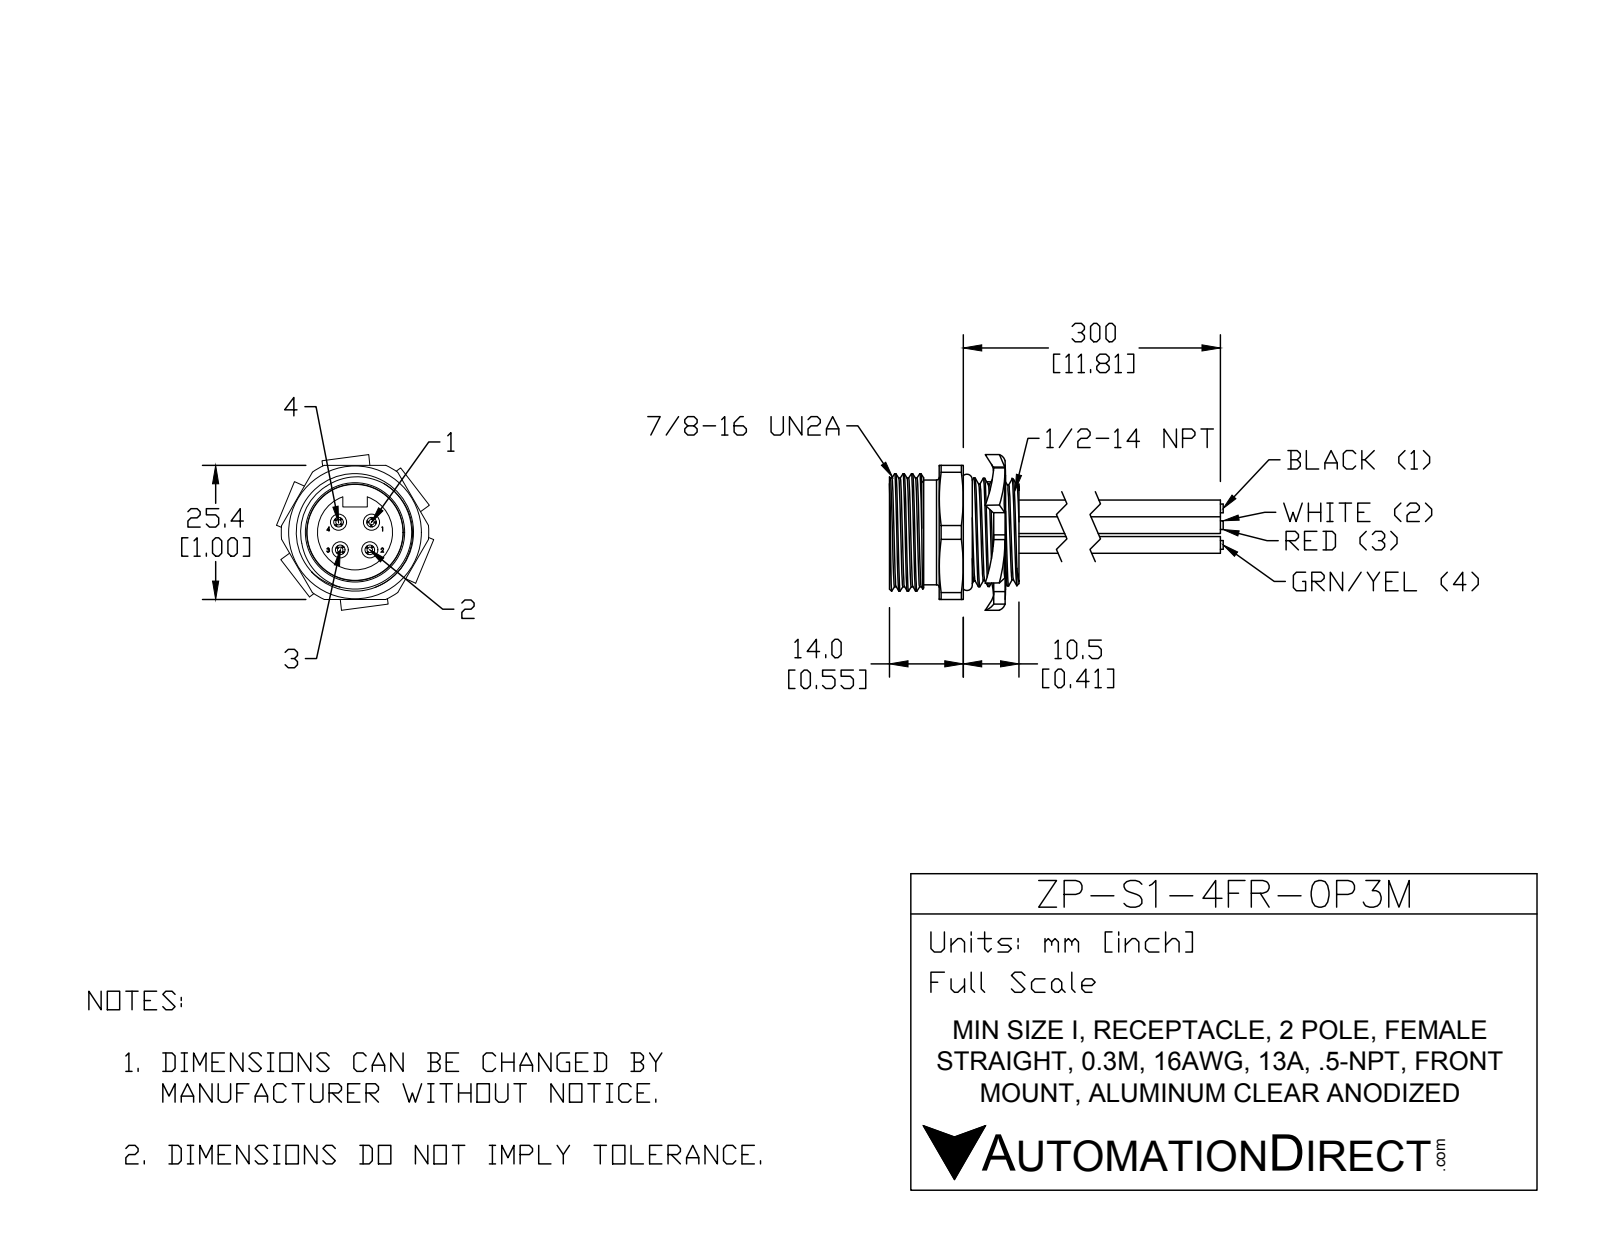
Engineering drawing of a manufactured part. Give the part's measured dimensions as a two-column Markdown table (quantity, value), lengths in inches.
| quantity | value |
| --- | --- |
| part name | MIN-4FR-ZZ |
| STEP written by | SolidWorks 2015 (AUTOMOTIVE_DESIGN) |
| units | inches |
| bodies | 1 solid, 229 faces (85 planar, 69 cylindrical, 75 other) |
| overall size | 1.949 × 1.172 × 1.161 |
| volume | 0.558 in³ |
| surface area | 9.622 in² |
| round holes (diameter × count) | 0.12 × 4, 0.72 × 1, 0.772 × 1 |
| round bosses / shafts (diameter × count) | 0.125 × 4, 0.999 × 1, 0.875 × 1, 0.811 × 1, 0.78 × 1, 0.716 × 1, 0.714 × 1, 0.56 × 1 |
| partial cylindrical surfaces (radius × count) | 0.55 × 1 |
| main face-to-face distances | 0.595, 1, 0.18, 0.415, 0.307, 0.487, 0.902, 0.276, 0.031, 0.211 |
| hole center spacings | 0.144, 0.17, 0.206, 0.311, 0.22, 0.246 |
